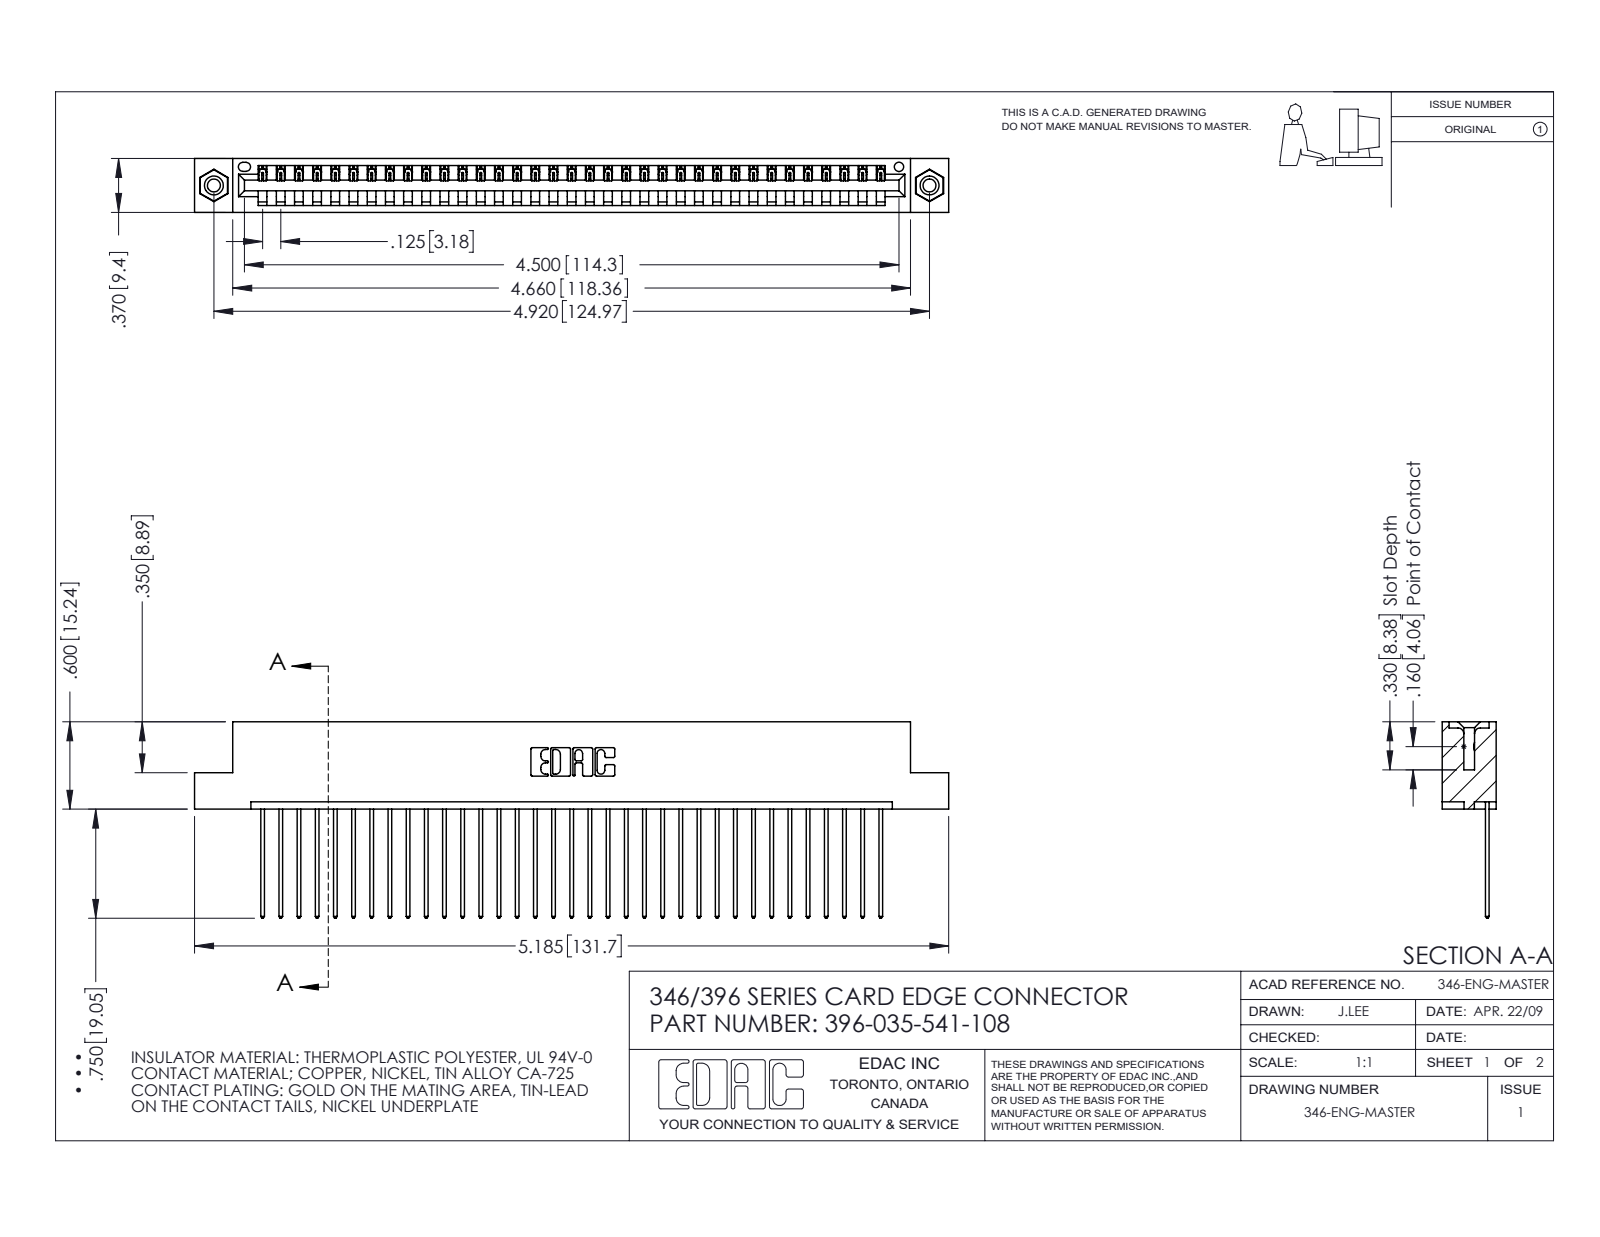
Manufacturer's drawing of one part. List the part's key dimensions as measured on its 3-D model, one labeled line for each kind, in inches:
Part name (STEP PRODUCT): 396-035-541-108; 345-292-001_345-293-141; 345-250-001_345-250-003-102; 346 Part_Flush Mounting Lugs - 0.156 Dia-TI
STEP written by: SolidWorks 2016 (CONFIG_CONTROL_DESIGN)
Units: inches
Bodies: 38 solids, 2212 faces (1508 planar, 688 cylindrical, 16 other)
Overall size (bounding box): 5.185 × 1.35 × 0.37
Volume: 0.773 in³ · Surface area: 25.53 in²
Round holes (diameter × count): ⌀0.089 ×2, ⌀0.125 ×2, ⌀0.156 ×2, ⌀0.064 ×1
Round bosses / shafts (diameter × count): ⌀0.155 ×2
Partial cylindrical surfaces — rounded edges, fillets, slot ends (radius × count): R0.006 ×70, R0.01 ×70, R0.01 ×22, R0.007 ×6, R0.031 ×6, R0.026 ×3, R0.031 ×2, R0.04 ×2
Main face-to-face distances: 0.048, 0.322, 0.37, 0.25, 0.072, 0.298, 0.025, 0.148, 0.222, 0.1
Hole centre spacings: 0.246, 4.711, 4.92
